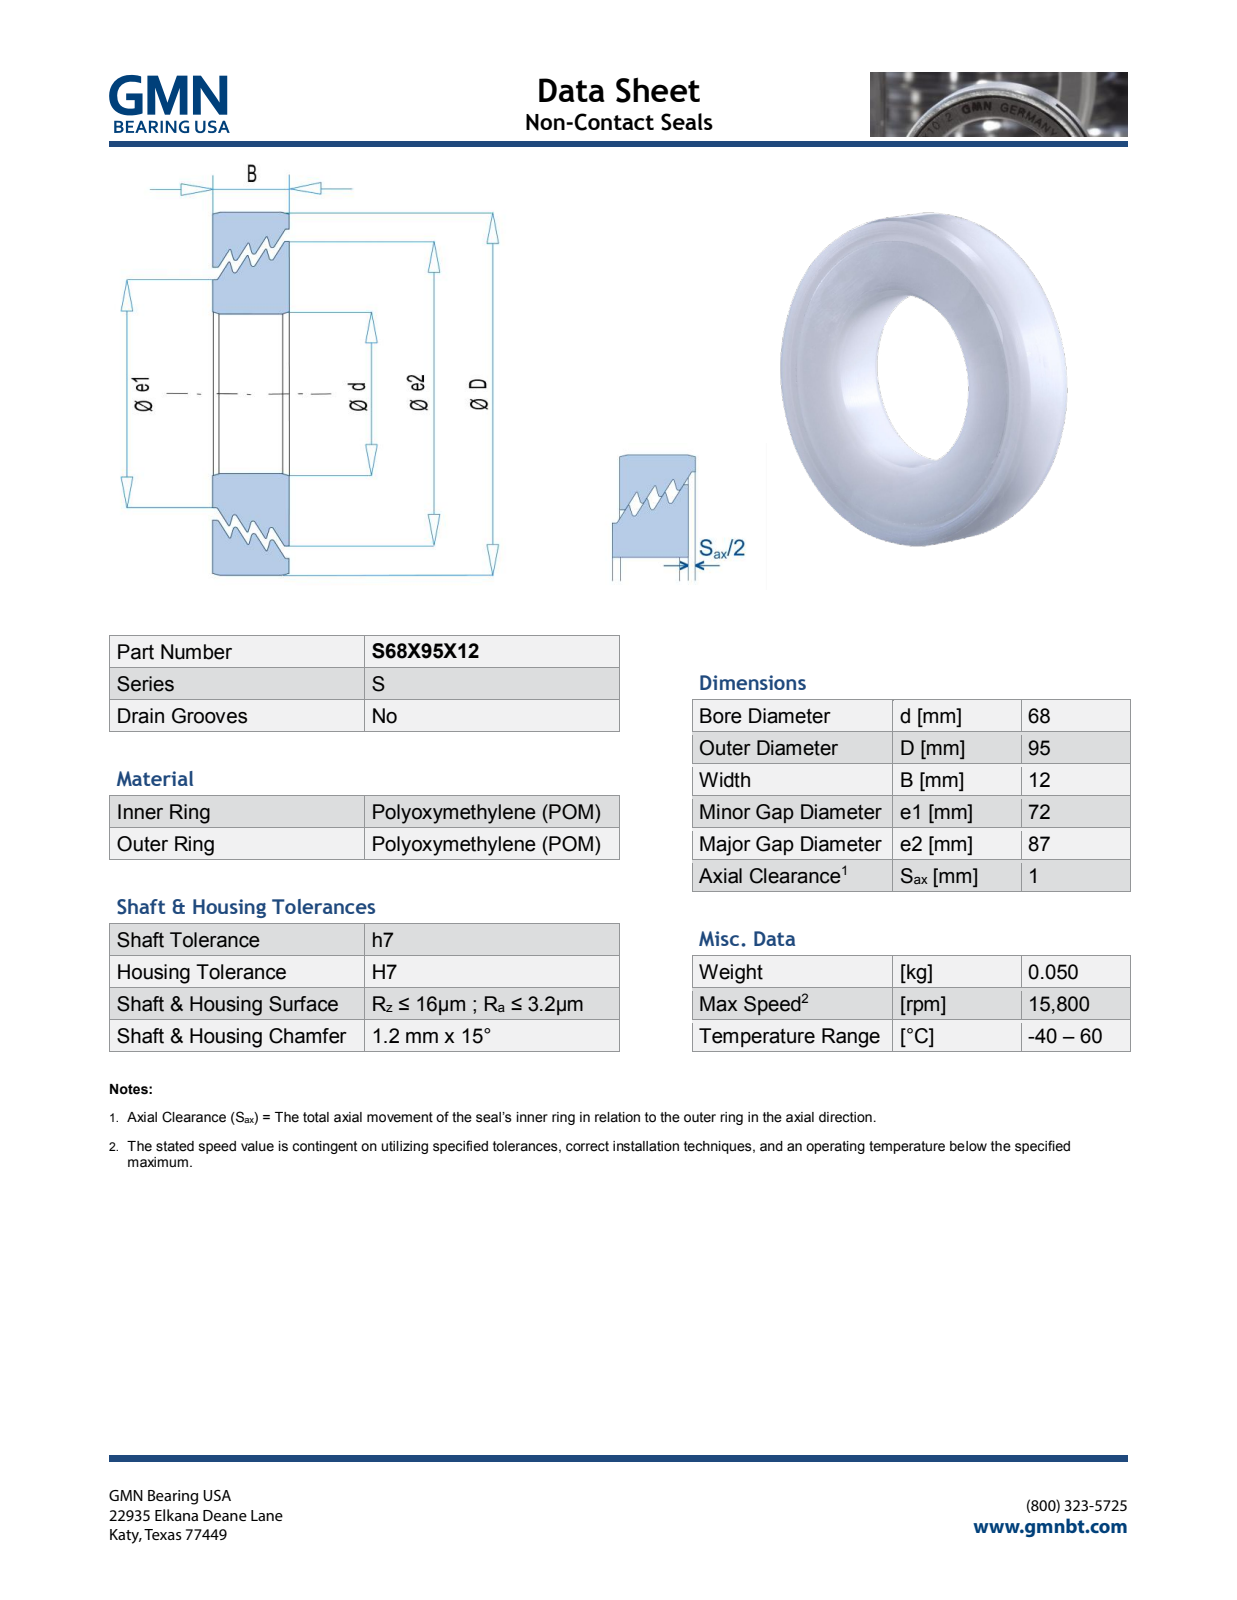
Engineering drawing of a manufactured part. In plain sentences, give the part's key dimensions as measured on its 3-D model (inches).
The part is named "S68X95X12_PRT". Its 3-D file was written by "PRO/ENGINEER BY PARAMETRIC TECHNOLOGY CORPORATION, 2013150 (AUTOMOTIVE_DESIGN)". It is 2 solids with 710 faces: 630 planar, 12 cylindrical and 68 other. Overall it measures 3.74 by 3.74 by 0.475 inches. Its volume is 2.372 cubic inches and its surface area 38.58 square inches. Round holes: 1 of diameter 2.677, 1 of diameter 2.899, 1 of diameter 3.489. Round bosses or shafts: 1 of diameter 3.74, 1 of diameter 3.425, 1 of diameter 2.835. The main face-to-face distances are 0.472, 0.475, 0.013, 0.013, 0.102, 0.089, 0.072, 0.076, 0.043, 0.03.
